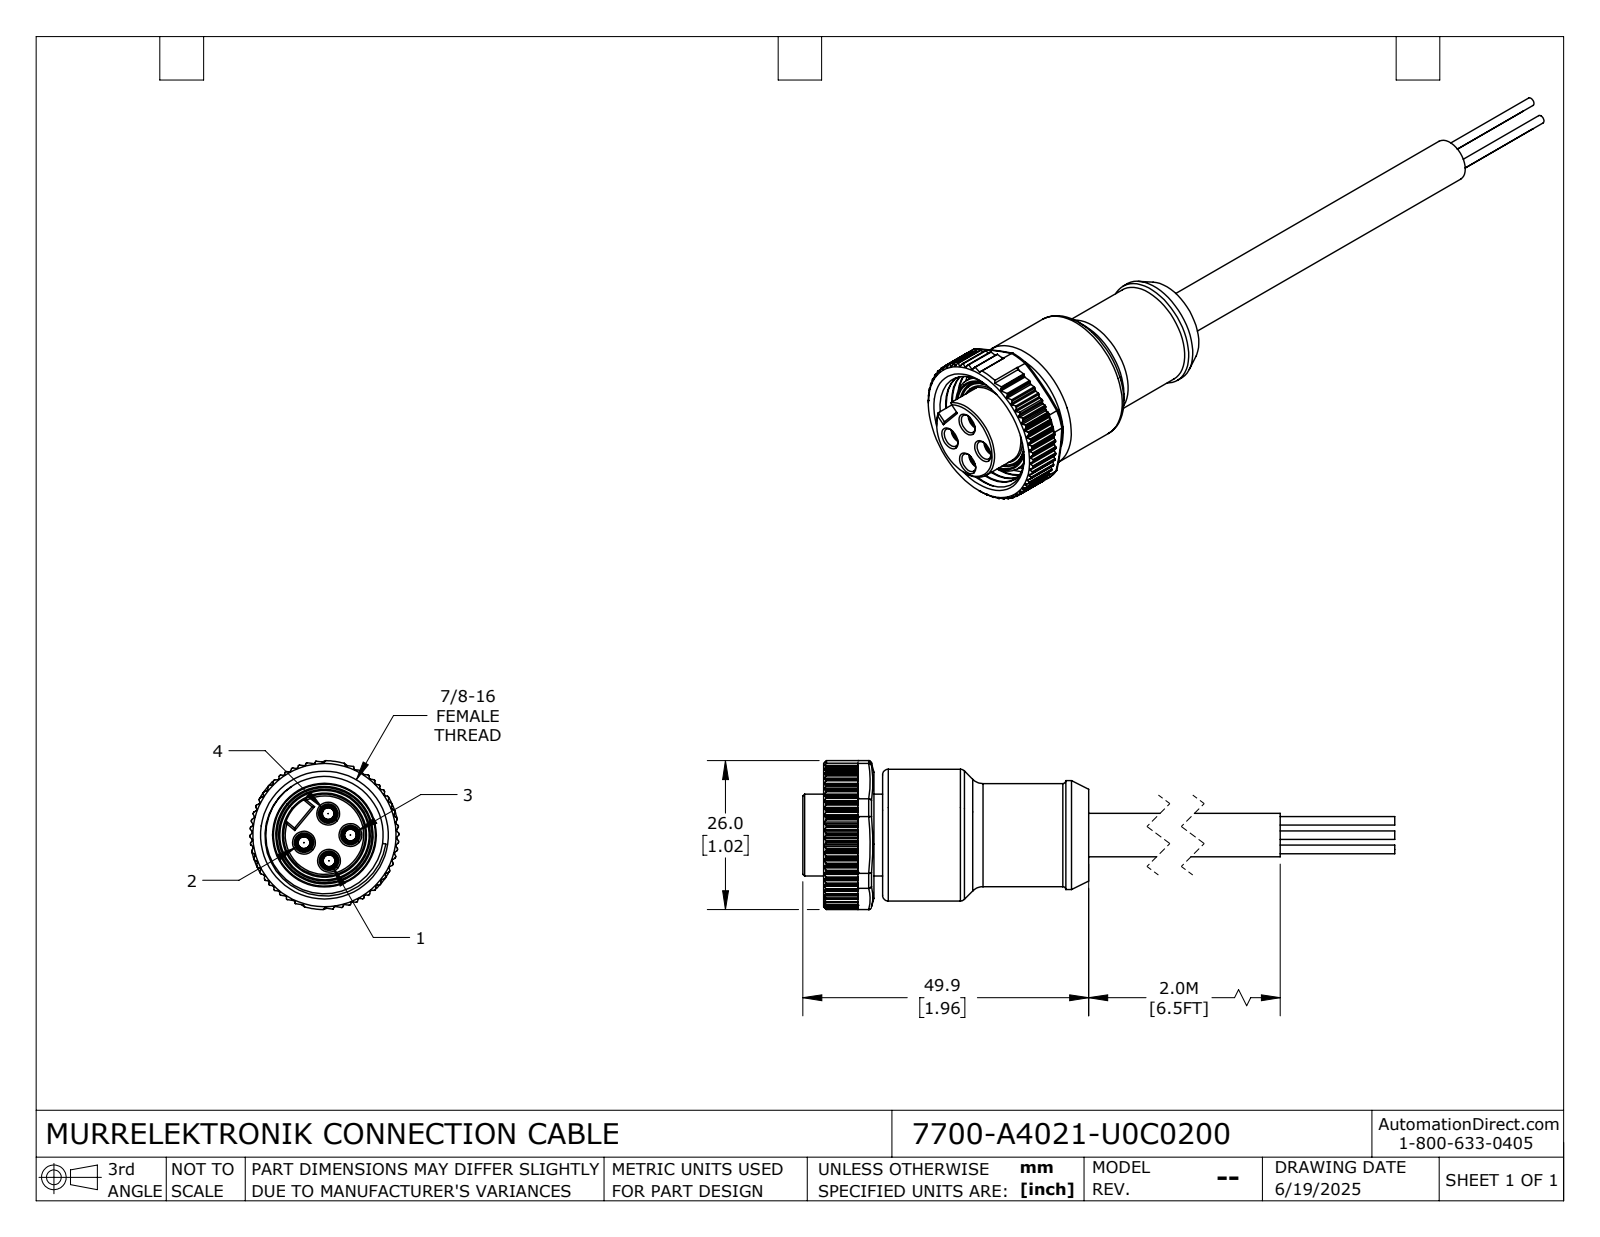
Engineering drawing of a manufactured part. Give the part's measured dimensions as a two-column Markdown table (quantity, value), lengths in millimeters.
| quantity | value |
| --- | --- |
| part name | 7700-A4021-U0C0200 |
| STEP written by | SolidWorks 2024 (CONFIG_CONTROL_DESIGN) |
| units | millimeters |
| bodies | 1 solid, 674 faces (296 planar, 293 cylindrical, 85 other) |
| overall size | 139.9 × 26 × 26 |
| volume | 18 784 mm³ |
| surface area | 8 325 mm² |
| round holes (diameter × count) | 2.05 × 4, 3 × 4, 3.4 × 4, 15.5 × 1, 15.6 × 1, 20.5 × 1, 22.23 × 1 |
| round bosses / shafts (diameter × count) | 1.5 × 4, 23 × 1, 19 × 1, 18.1 × 1, 18 × 1, 17.8 × 1, 14.3 × 1, 7.6 × 1 |
| partial cylindrical surfaces (radius × count) | 0.2 × 126, 0.3 × 16, 0.1 × 4, 0.73 × 4, 13 × 1 |
| main face-to-face distances | 1.5, 37.5, 36, 3.6, 8.8, 10.3, 46.3, 12.4, 13.9, 49.9 |
| hole center spacings | 3.81, 4.54, 8.22, 5.39, 5.4, 5.84, 6.6 |
